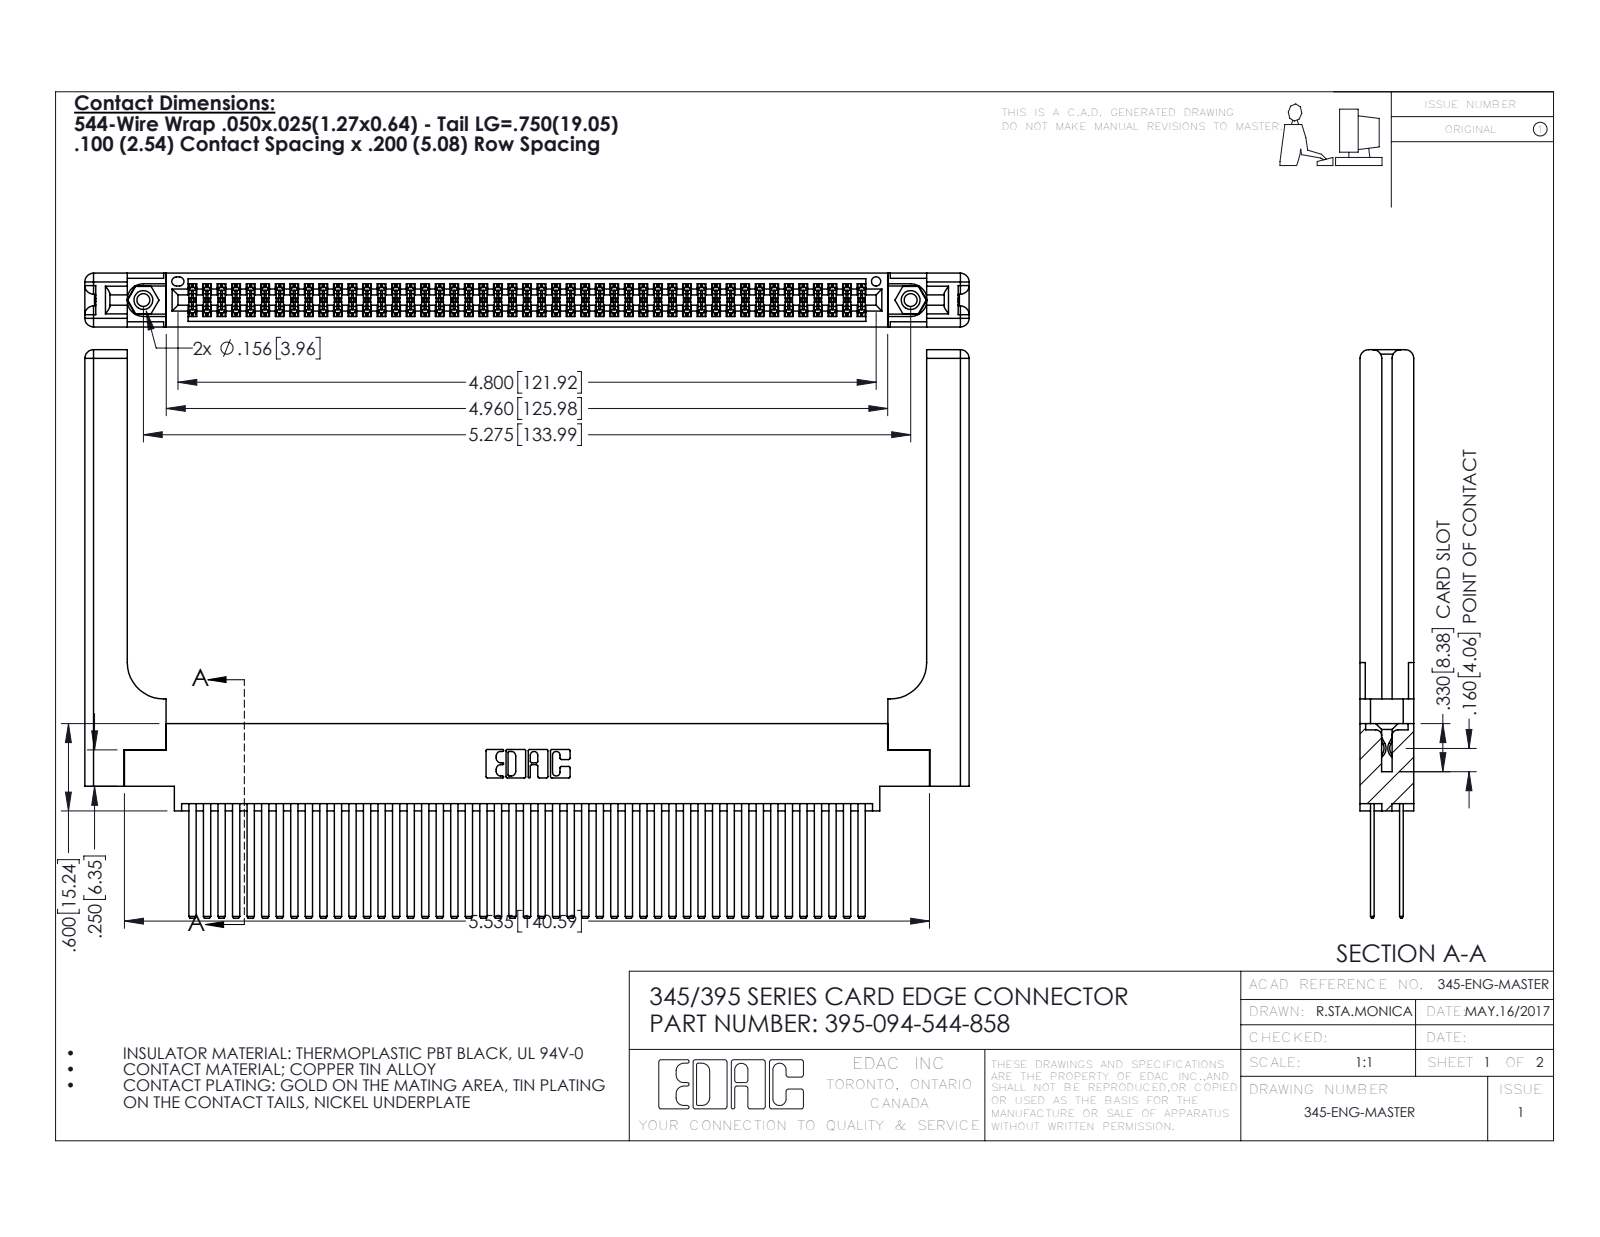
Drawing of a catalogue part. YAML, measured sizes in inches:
part_name: "345-250-001_345-250-001-102; 345-292-001_345-293-144; 345-220-058_345-220-058; 395-094-544-858 (+1 more)"
step_written_by: "SolidWorks 2016 (CONFIG_CONTROL_DESIGN)"
units: inches
bodies: {solids: 99, faces: 4522, planar: 2958, cylindrical: 1504, other: 60}
overall_size: [6.079, 3.907, 0.37]
volume: 1.509
surface_area: 51.43
round_holes:
  - {diameter: 0.089, count: 2}
  - {diameter: 0.125, count: 2}
  - {diameter: 0.156, count: 2}
  - {diameter: 0.064, count: 1}
round_bosses_or_shafts:
  - {diameter: 0.155, count: 2}
partial_cylinders:
  - {radius: 0.006, count: 141}
  - {radius: 0.01, count: 22}
  - {radius: 0.06, count: 16}
  - {radius: 0.007, count: 6}
  - {radius: 0.031, count: 6}
  - {radius: 0.026, count: 3}
  - {radius: 0.014, count: 2}
  - {radius: 0.019, count: 2}
face_to_face_distances: [0.072, 0.298, 0.098, 0.272, 0.025, 0.2, 0.37, 0.225, 0.175, 0.148]
hole_center_spacings: [0.27, 5.039, 5.275]
